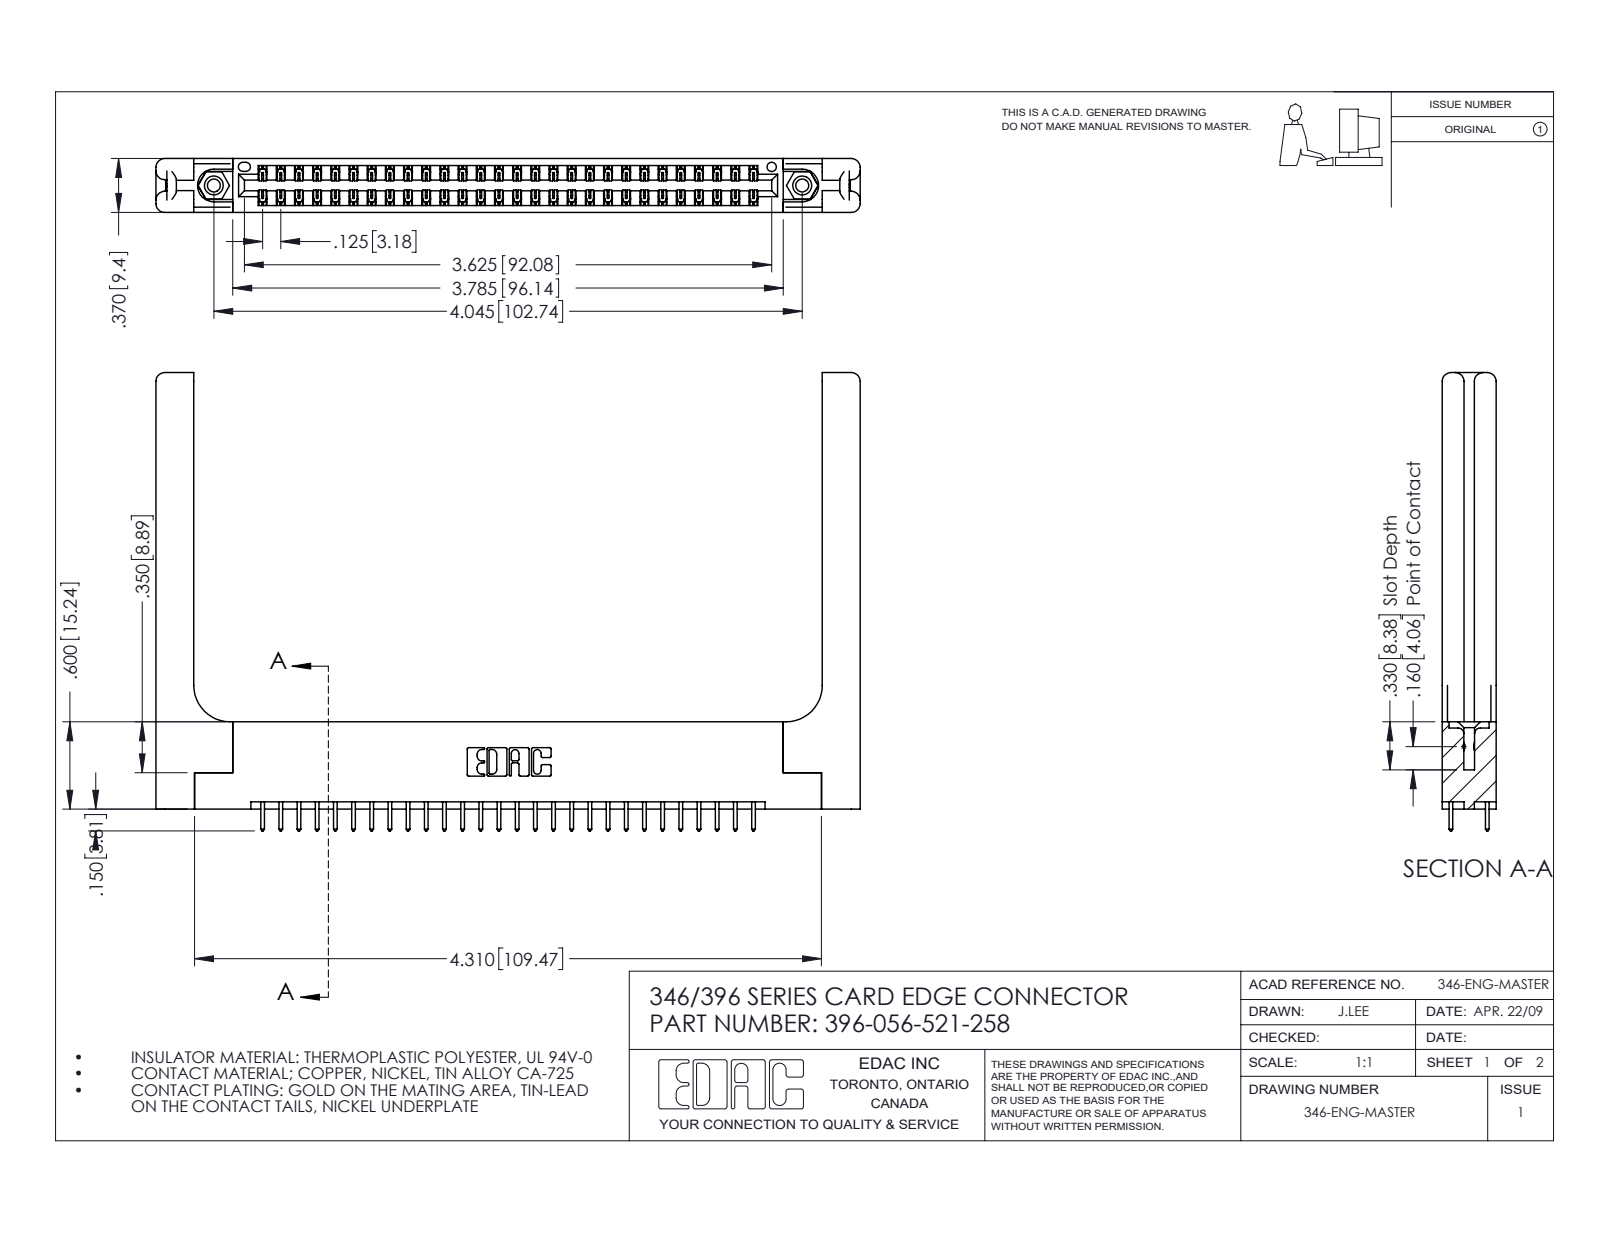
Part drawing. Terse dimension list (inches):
name: 346 Part_Flush Mounting Lugs - 0.156 Dia-TH; 396-056-521-258; 345-250-001_345-250-001-102; 346-220-058_345-220-058 (+1 more)
written by: SolidWorks 2016 (CONFIG_CONTROL_DESIGN)
unit: in
bodies: 61 solids, 3290 faces (2184 planar, 1046 cylindrical, 60 other)
size: 4.841 × 3.15 × 0.37
volume: 1.181 in³; area: 32.39 in²
holes: 2× ⌀0.089, 2× ⌀0.125, 2× ⌀0.156, 1× ⌀0.064
bosses: 2× ⌀0.155
rounds: 84× R0.006, 56× R0.01, 22× R0.01, 16× R0.06, 6× R0.007, 6× R0.031, 3× R0.026, 2× R0.014
face distances: 0.37, 0.048, 0.322, 0.072, 0.148, 0.15, 0.25, 0.025, 0.298, 0.275
hole spacings: 0.246, 3.837, 4.045
